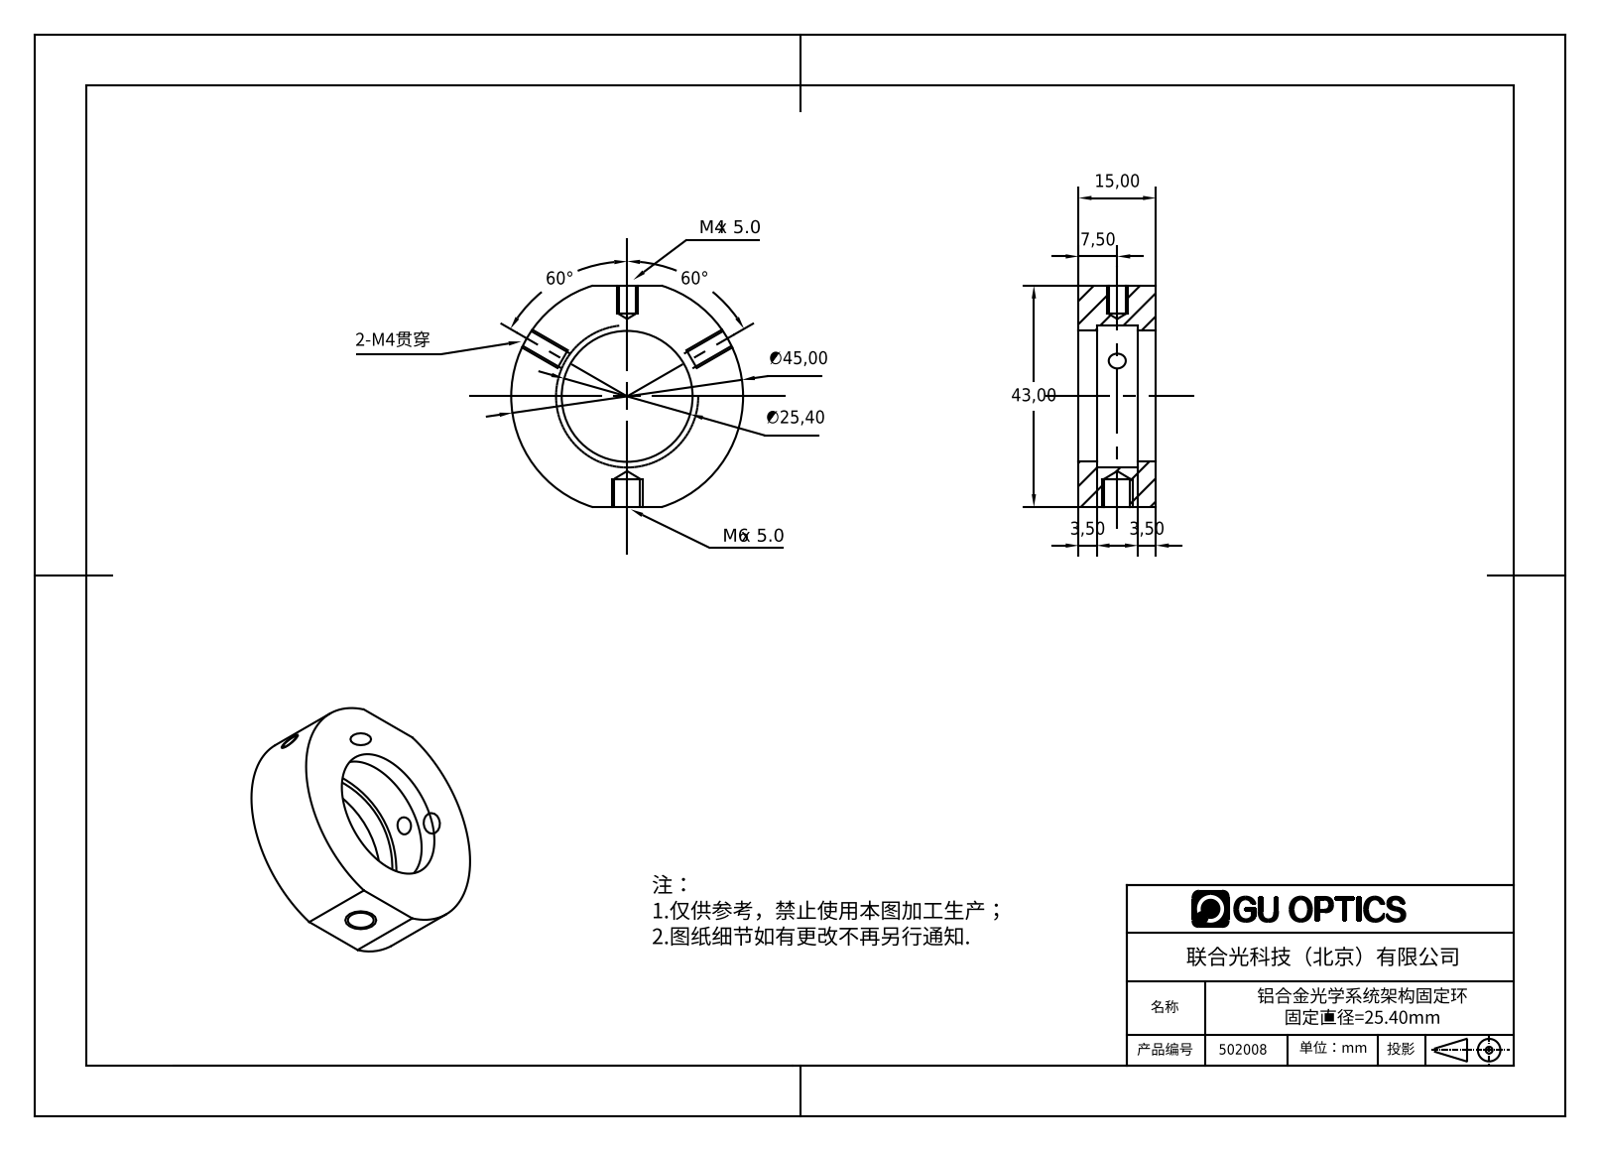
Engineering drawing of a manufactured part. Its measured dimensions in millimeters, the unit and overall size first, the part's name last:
Units: millimetres
Overall size (bounding box): 45 × 43 × 15
Round holes (diameter × count): ⌀3.3 ×3, ⌀5 ×1, ⌀25.4 ×1, ⌀27.6 ×1
Round bosses / shafts (diameter × count): ⌀45 ×1
Main face-to-face distances: 15, 3.5, 11.5, 43, 8
Volume: 14 940 mm³ · Surface area: 5 977 mm²
Bodies: 1 solid, 27 faces (6 planar, 17 cylindrical, 4 other)
Part name (STEP PRODUCT): 502008
STEP written by: SolidWorks 2016 (CONFIG_CONTROL_DESIGN)
